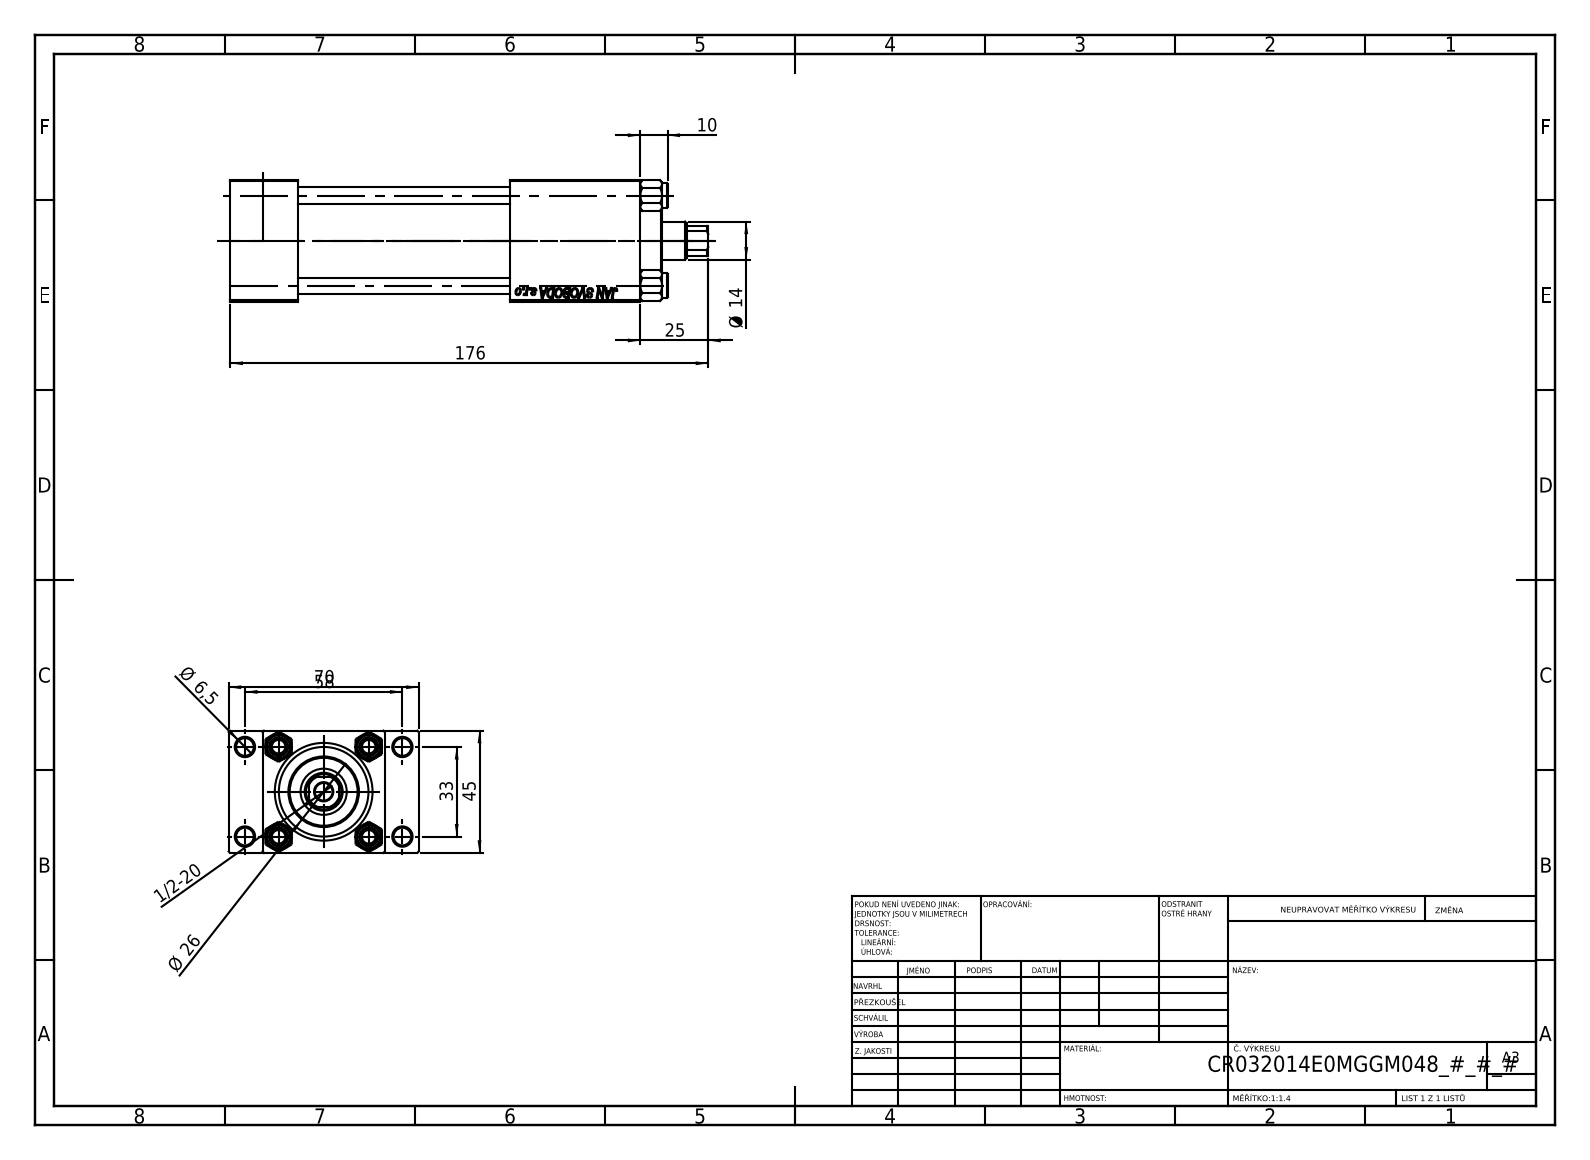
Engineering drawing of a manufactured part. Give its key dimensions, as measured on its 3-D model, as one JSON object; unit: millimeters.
{"part_name": "V215CR_TYCINKA_E; NUT_M5_E; V215CR_VCP_E; V215_VC_A (+1 more)", "step_written_by": "SolidWorks 2019 (CONFIG_CONTROL_DESIGN)", "units": "millimeters", "bodies": {"solids": 11, "faces": 1136, "planar": 497, "cylindrical": 87, "other": 552}, "overall_size": [176, 70, 45], "volume_mm3": 236786, "surface_area_mm2": 85573, "round_holes": [[6.5, 5], [6, 4], [7, 2], [13.16, 2], [20, 2], [14, 1], [17, 1], [24, 1], [32, 1], [33, 1]], "round_bosses_or_shafts": [[9, 4], [38, 1], [26, 1]], "partial_cylinders_radius": [[6.5, 1]], "face_to_face_distances": [45, 25, 12.5, 57.5, 48, 151, 126, 70, 103, 78], "hole_center_spacings": [12.4, 23.48, 33.2, 33.37, 35.35, 45.6, 56.35, 33]}
